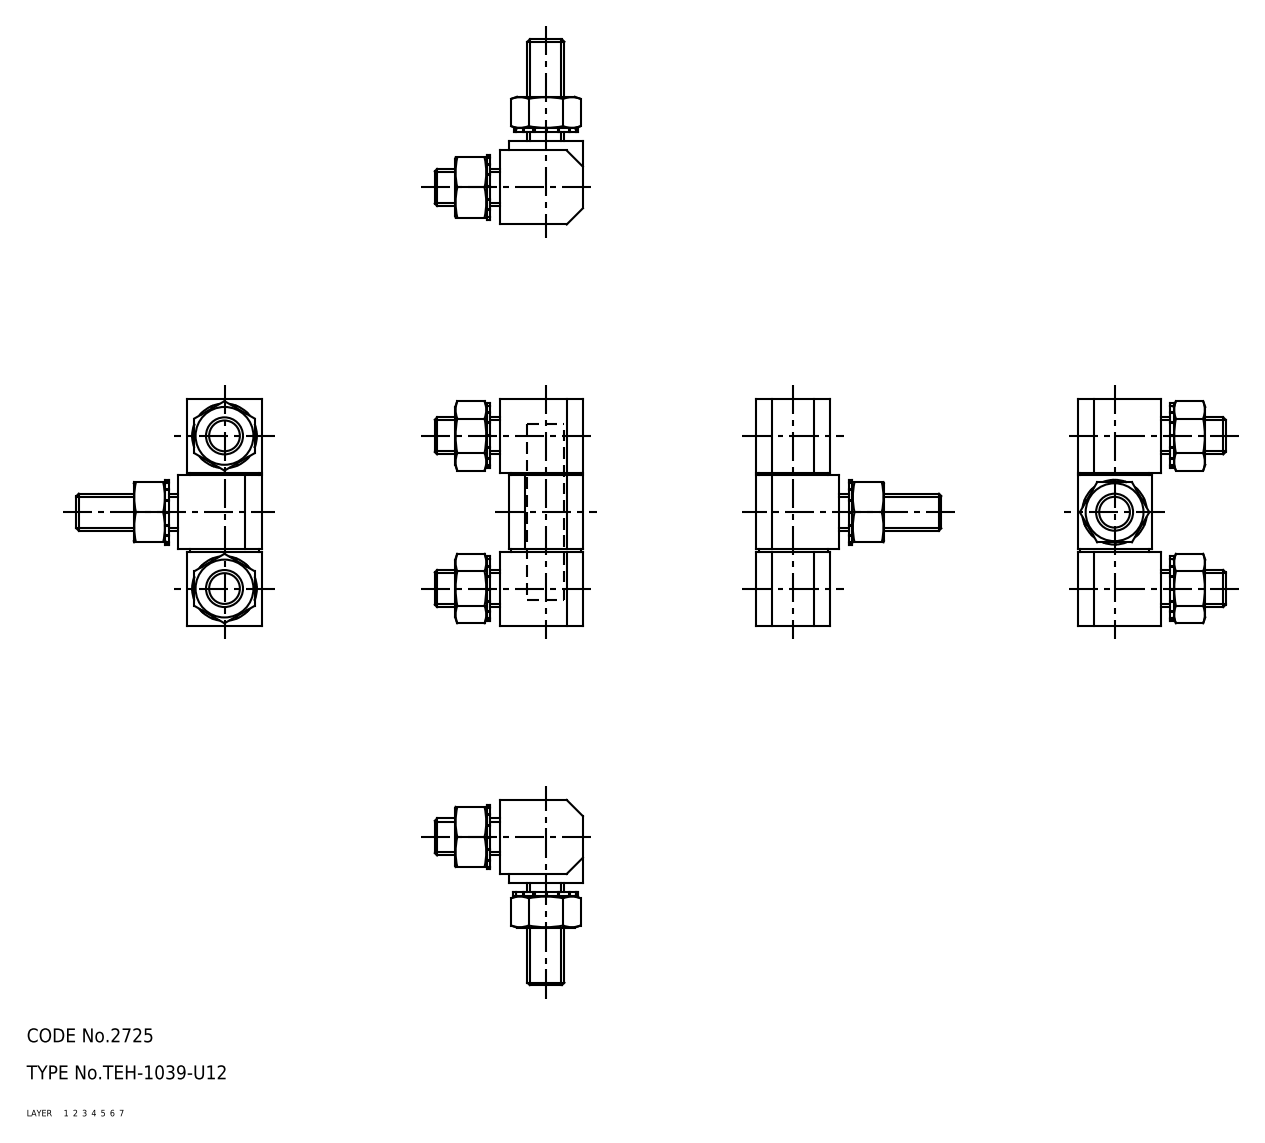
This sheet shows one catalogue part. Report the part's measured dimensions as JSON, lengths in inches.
{"part_name": "washer_B; nut; hinge pieces_A; washer_A (+3 more)", "step_written_by": "CADfix (AUTOMOTIVE_DESIGN)", "units": "inches", "bodies": {"solids": 12, "faces": 123, "planar": 0, "cylindrical": 0, "other": 123}, "overall_size": [1.929, 1.575, 1.26], "volume_in3": 1.092, "surface_area_in2": 17.4}
